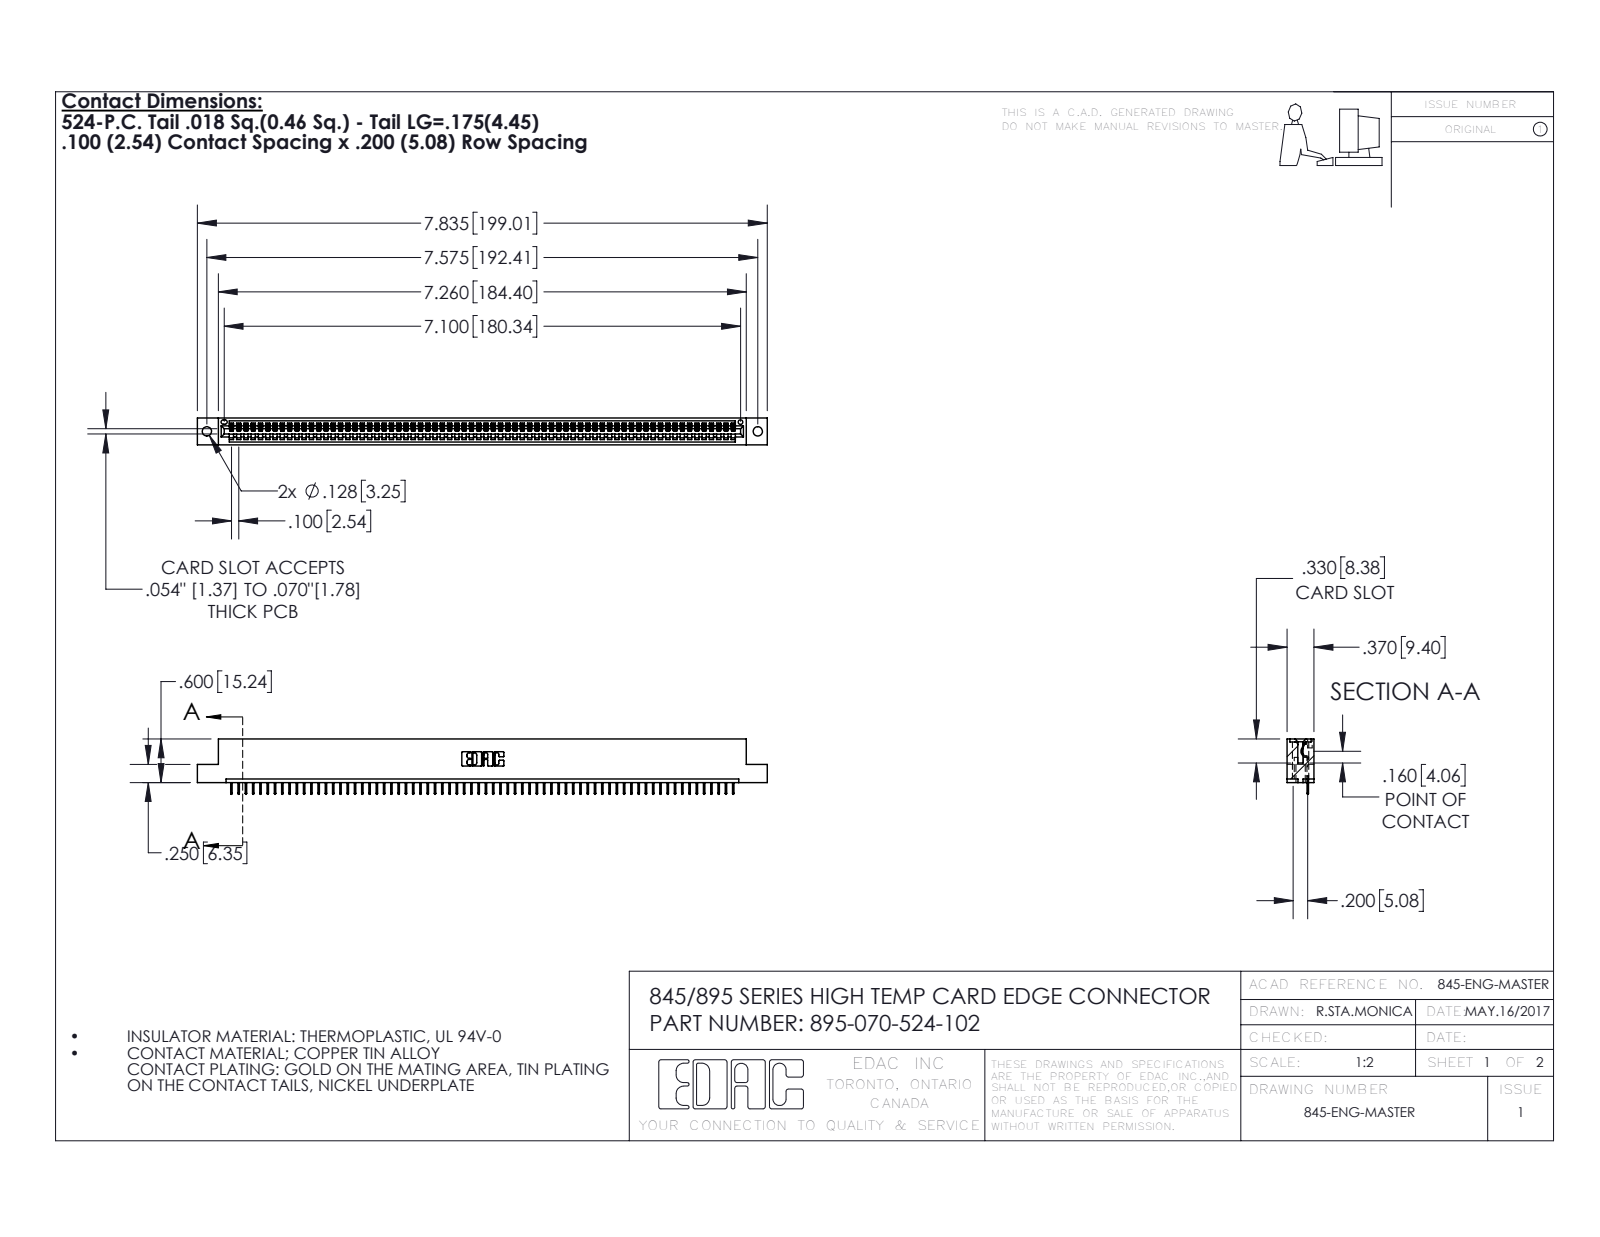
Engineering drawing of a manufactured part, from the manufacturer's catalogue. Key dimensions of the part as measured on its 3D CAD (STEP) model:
Part name (STEP PRODUCT): 345-292-001_345-293-124; 395-070-524-102; 345 Part_Flush Mounting Lugs - 0.128 Dia
STEP written by: SolidWorks 2016 (CONFIG_CONTROL_DESIGN)
Units: inches
Bodies: 71 solids, 4466 faces (3300 planar, 1166 cylindrical, 0 other)
Overall size (bounding box): 7.835 × 0.762 × 0.37
Volume: 1.148 in³ · Surface area: 37.56 in²
Round holes (diameter × count): ⌀0.128 ×2, ⌀0.064 ×1
Partial cylindrical surfaces — rounded edges, fillets, slot ends (radius × count): R0.006 ×140, R0.01 ×22, R0.007 ×6, R0.031 ×6, R0.026 ×3, R0.031 ×2, R0.04 ×2, R0.014 ×1
Main face-to-face distances: 0.298, 0.072, 0.37, 0.2, 0.098, 0.272, 0.025, 0.225, 0.072, 0.149
Hole centre spacings: 0.27, 7.339, 7.575
